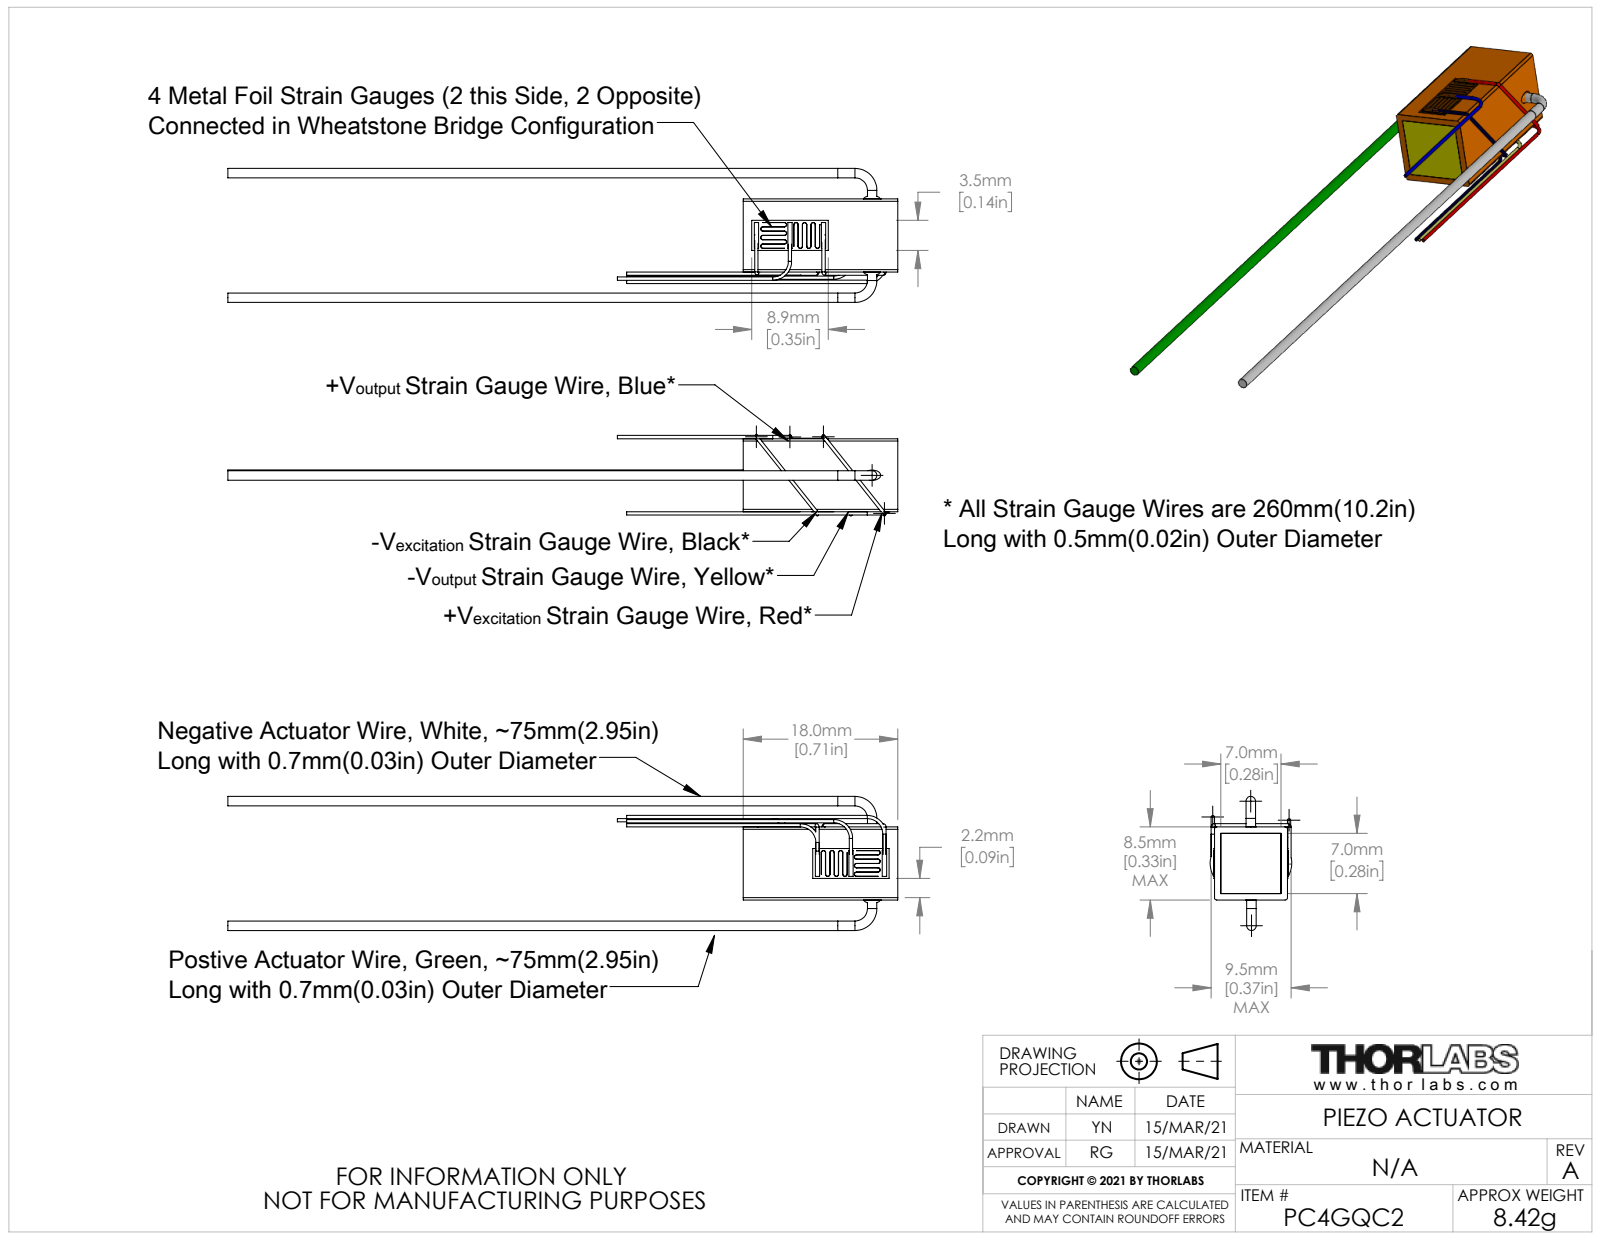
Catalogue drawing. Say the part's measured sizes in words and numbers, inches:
The part is named "CTN017170". Its 3-D file was written by "SolidWorks 2018 (AUTOMOTIVE_DESIGN)". It is 12 solids with 268 faces: 132 planar, 104 cylindrical and 32 other. Overall it measures 3.07 by 0.614 by 0.374 inches. Its volume is 0.09 cubic inches and its surface area 4.059 square inches. Round bosses or shafts: 12 of diameter 0.015, 4 of diameter 0.043. Partial cylindrical surfaces (rounded edges, fillets, slot ends): 24 of radius 0.009, 24 of radius 0.01, 4 of radius 0.011. The main face-to-face distances are 0.03, 0.305, 0.276, 0.335, 0.709, 0.031, 0.307, 0.337, 0.339, 0.02.
